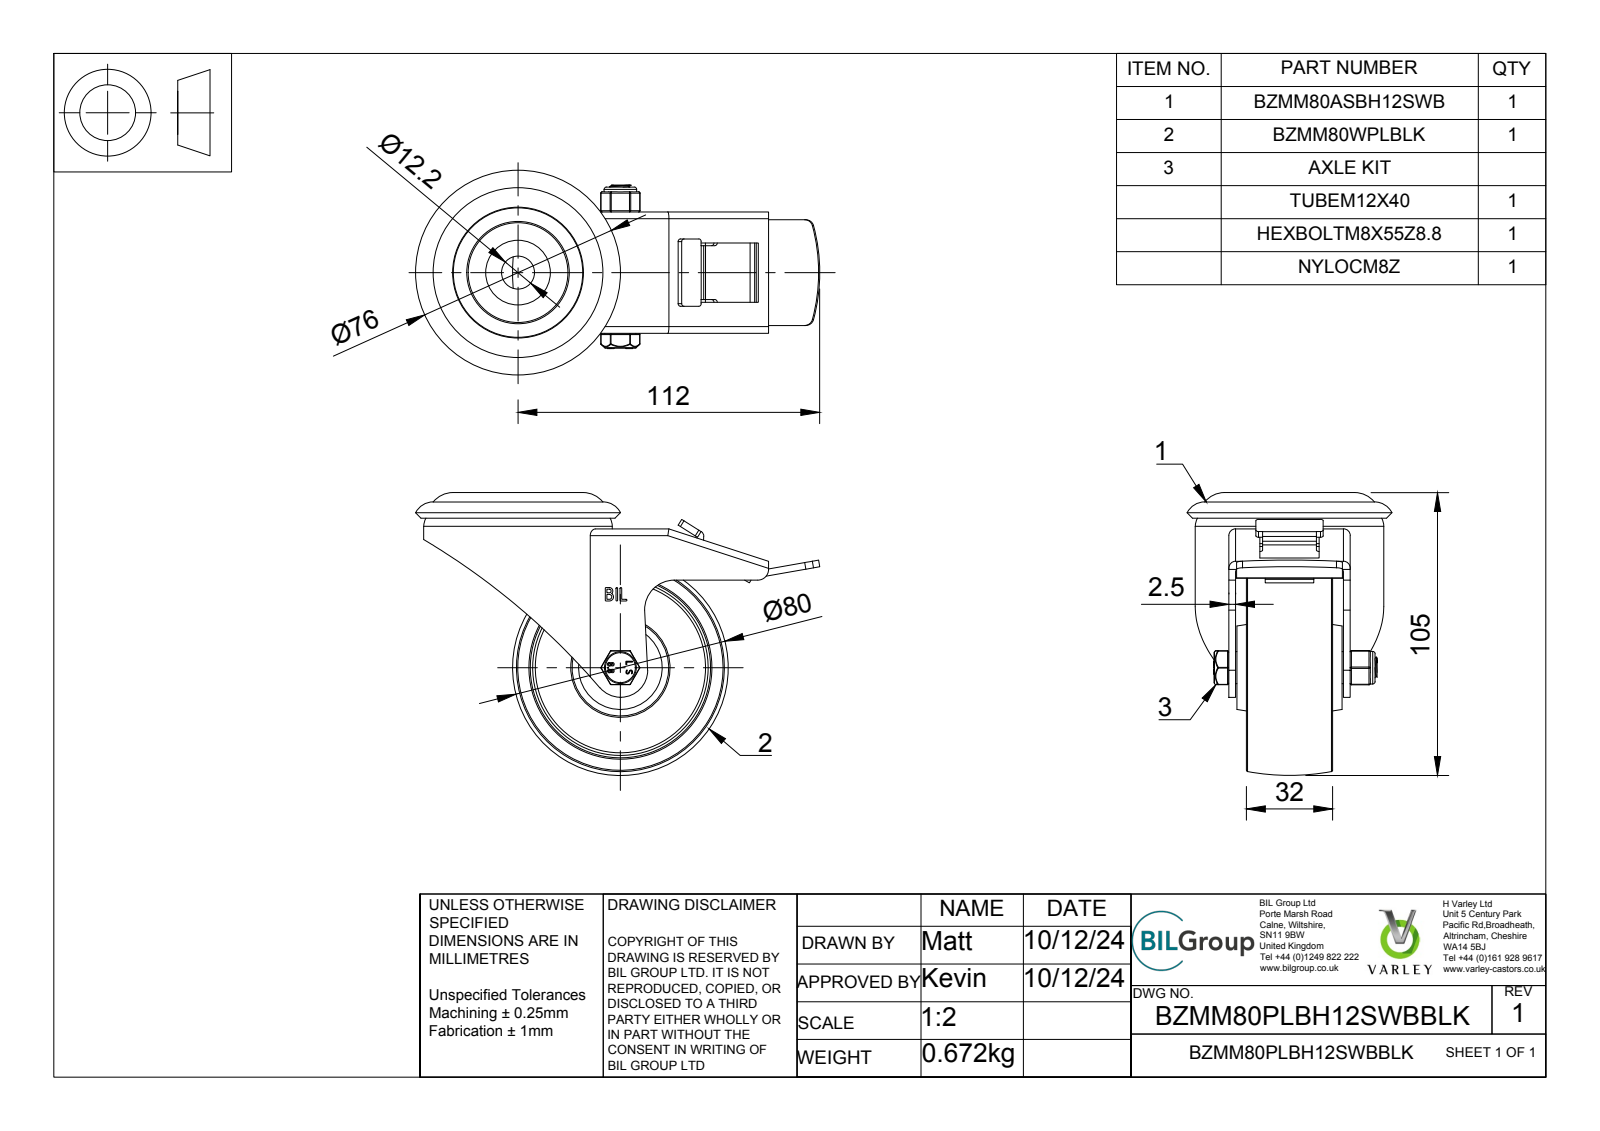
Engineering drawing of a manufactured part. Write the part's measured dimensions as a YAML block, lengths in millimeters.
part_name: "BZMM80PLBH12SWBBLK v3; BZMM80ASBH12SWB v1; ZINC PLATED, PRESSED STEEL HEAD; ZINC PLATED, PRESSED STEEL FORKS (+8 more)"
step_written_by: "Autodesk Translation Framework v13.20.0.188 (AP242_MANAGED_MODEL_BASED_3D_ENGINEERING_MIM_LF)"
units: millimeters
bodies: {solids: 9, faces: 589, planar: 275, cylindrical: 208, other: 106}
overall_size: [150, 105, 76]
volume: 167259
surface_area: 87645
round_holes:
  - {diameter: 0.66, count: 2}
  - {diameter: 12.2, count: 2}
  - {diameter: 8, count: 1}
  - {diameter: 8.2, count: 1}
  - {diameter: 8.4, count: 1}
  - {diameter: 8.6, count: 1}
  - {diameter: 65, count: 1}
  - {diameter: 72, count: 1}
round_bosses_or_shafts:
  - {diameter: 70, count: 1}
  - {diameter: 49.5, count: 1}
  - {diameter: 38, count: 1}
  - {diameter: 24, count: 1}
  - {diameter: 21.31, count: 1}
  - {diameter: 12.1, count: 1}
  - {diameter: 11.9, count: 1}
  - {diameter: 11.5, count: 1}
partial_cylinders:
  - {radius: 0.75, count: 48}
  - {radius: 0.5, count: 26}
  - {radius: 0.25, count: 12}
  - {radius: 1, count: 6}
  - {radius: 1.25, count: 6}
  - {radius: 2, count: 5}
  - {radius: 2.5, count: 5}
  - {radius: 0.33, count: 4}
face_to_face_distances: [2.5, 19, 26, 16.5, 23.5, 42.5, 7, 12.5, 6.5, 4]
hole_center_spacings: [3.22, 2.49]
